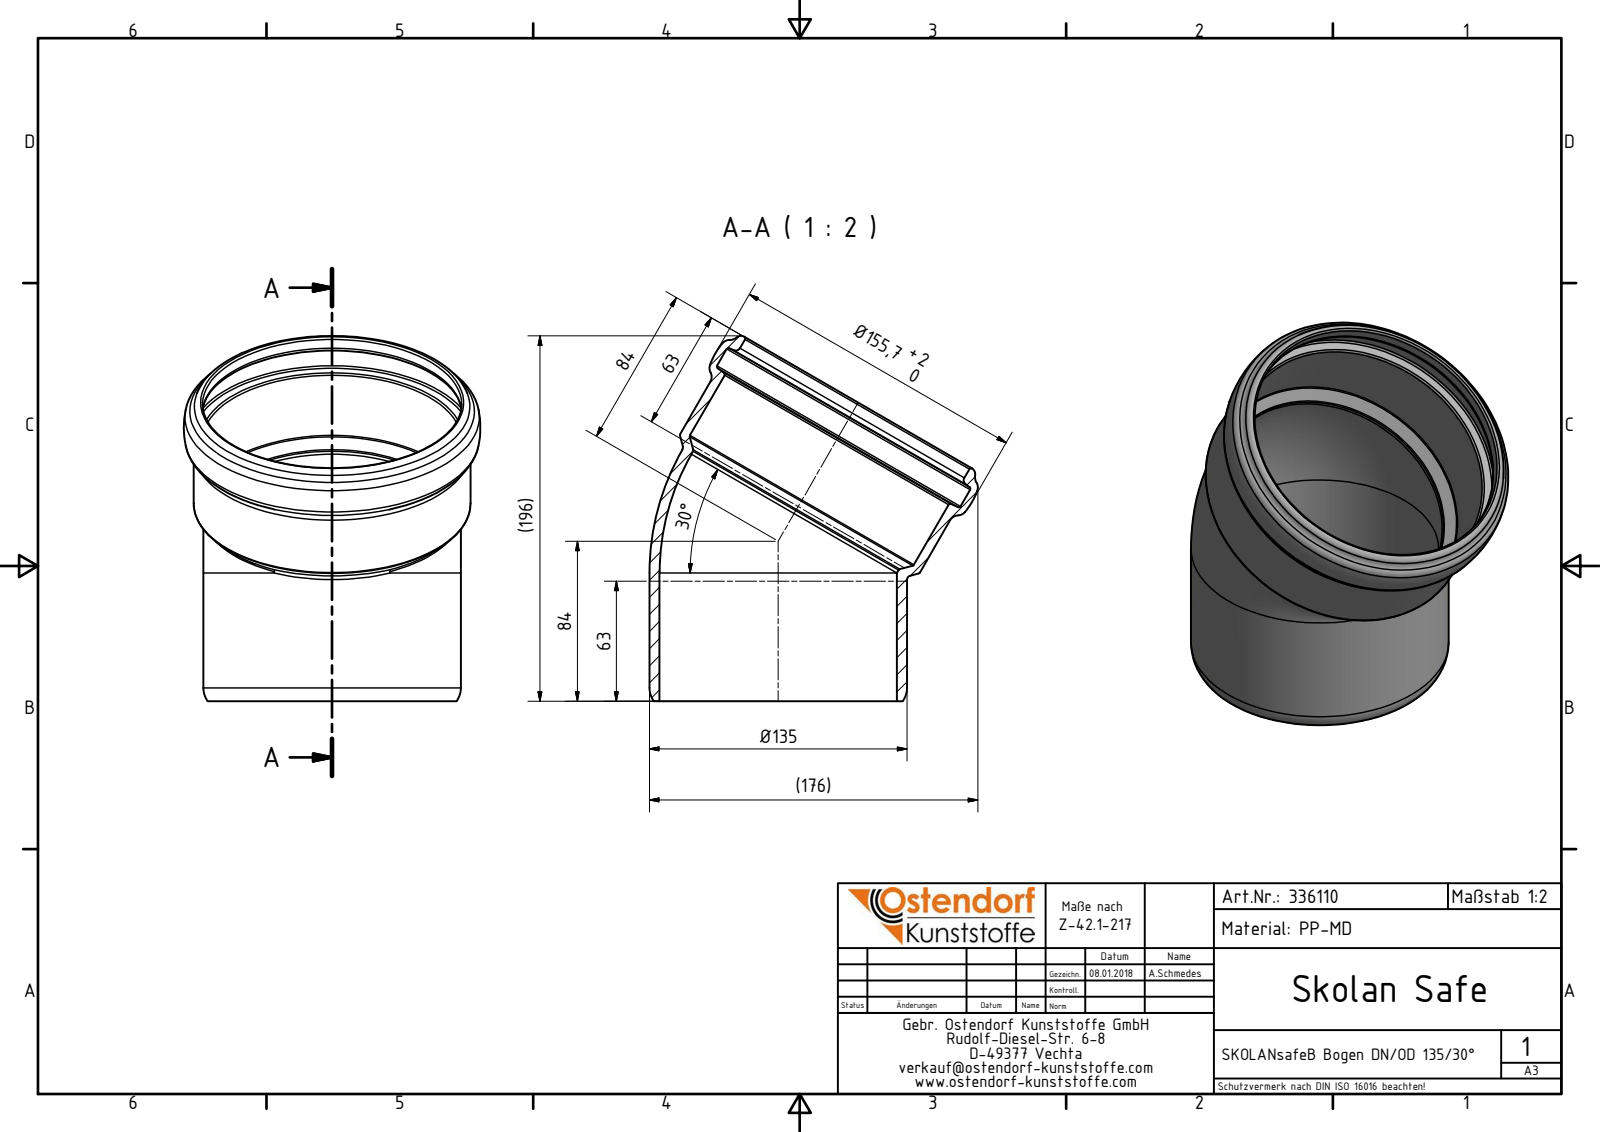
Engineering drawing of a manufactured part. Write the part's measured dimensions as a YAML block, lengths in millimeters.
part_name: "336110 SKOLANsafeB Bogen DN_OD 135_30°"
step_written_by: "Autodesk Inventor 2016 (AUTOMOTIVE_DESIGN)"
units: millimeters
bodies: {solids: 1, faces: 31, planar: 1, cylindrical: 7, other: 23}
overall_size: [191.74, 172.51, 155.7]
volume: 373092
surface_area: 151912
round_holes:
  - {diameter: 124.7, count: 2}
  - {diameter: 135.8, count: 1}
  - {diameter: 136.1, count: 1}
  - {diameter: 147.7, count: 1}
round_bosses_or_shafts:
  - {diameter: 145.4, count: 1}
  - {diameter: 135.3, count: 1}
